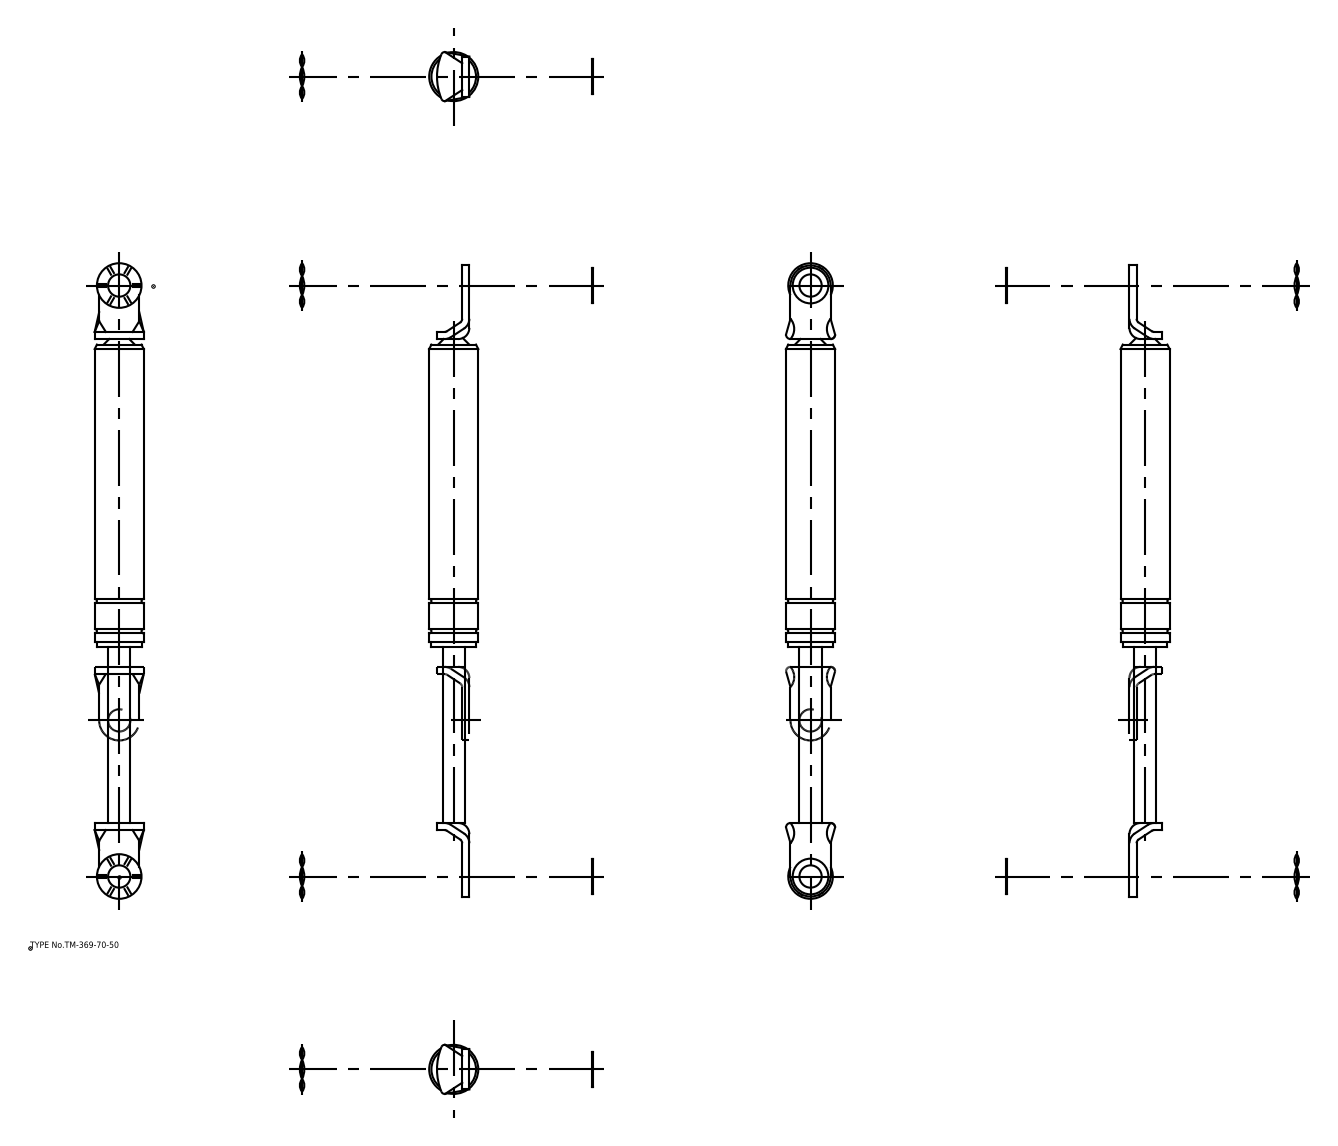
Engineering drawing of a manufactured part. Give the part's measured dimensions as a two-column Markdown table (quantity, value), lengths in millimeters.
| quantity | value |
| --- | --- |
| part name | ウェーブワッシャー; ワッシャー; 本体; 本体_div |
| STEP written by | spGate 16.7.1 (AUTOMOTIVE_DESIGN) |
| units | millimeters |
| bodies | 6 solids, 95 faces (43 planar, 44 cylindrical, 8 other) |
| overall size | 285 × 22.5 × 22.5 |
| volume | 63 400 mm³ |
| surface area | 18 303 mm² |
| round holes (diameter × count) | 10 × 2 |
| round bosses / shafts (diameter × count) | 20 × 3, 16 × 2, 22.5 × 1, 22 × 1, 10 × 1 |
| partial cylindrical surfaces (radius × count) | 4.4 × 2, 5 × 2, 9 × 2, 26.32 × 1 |
| main face-to-face distances | 3.2, 2, 5.2, 5.7, 220.2, 3.7, 0.5, 141.2, 82.2, 223.4 |
| hole center spacings | 265 |
